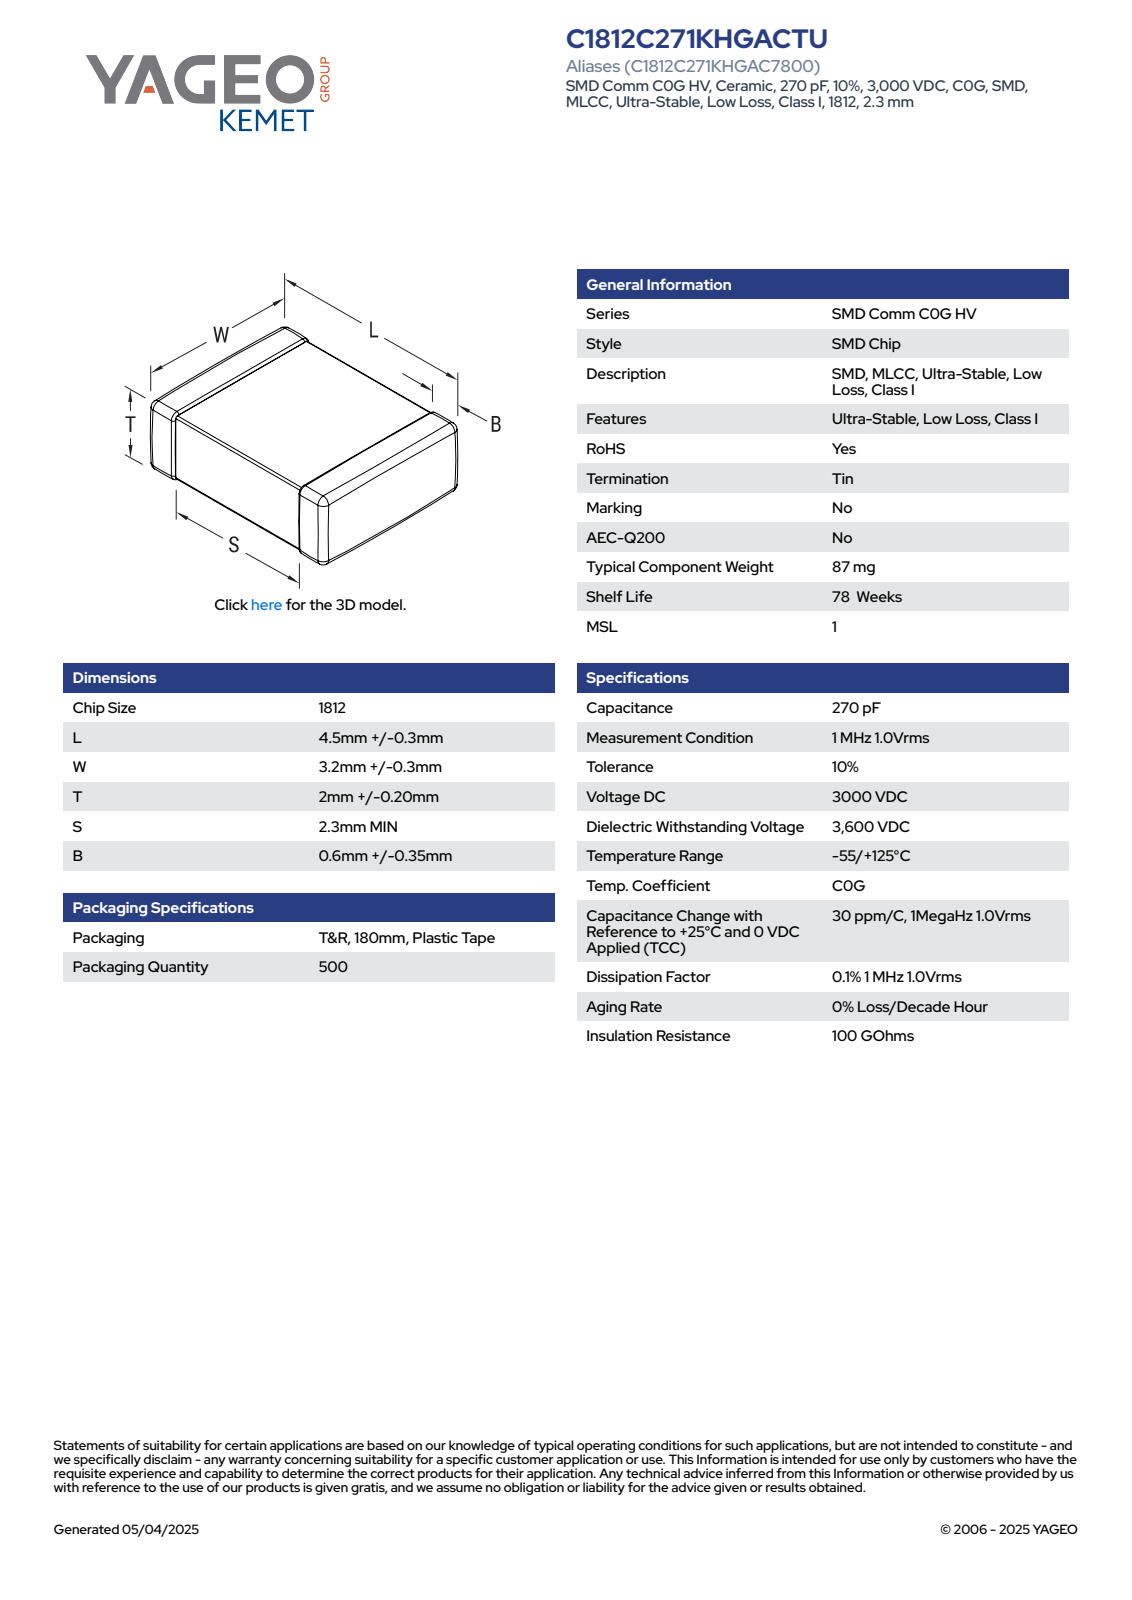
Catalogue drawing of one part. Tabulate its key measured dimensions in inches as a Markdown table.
| quantity | value |
| --- | --- |
| part name | CCS_CCSTD_1812_L4.8W3.5T2.2B0.6 |
| STEP written by | SolidWorks 2021 (AUTOMOTIVE_DESIGN) |
| units | inches |
| bodies | 4 solids, 125 faces (71 planar, 38 cylindrical, 16 other) |
| overall size | 0.189 × 0.138 × 0.087 |
| volume | 0.002 in³ |
| surface area | 0.11 in² |
| main face-to-face distances | 0.084, 0.081, 0.189, 0.135, 0.132, 0.087, 0.138, 0.082, 0.107, 0.102 |
